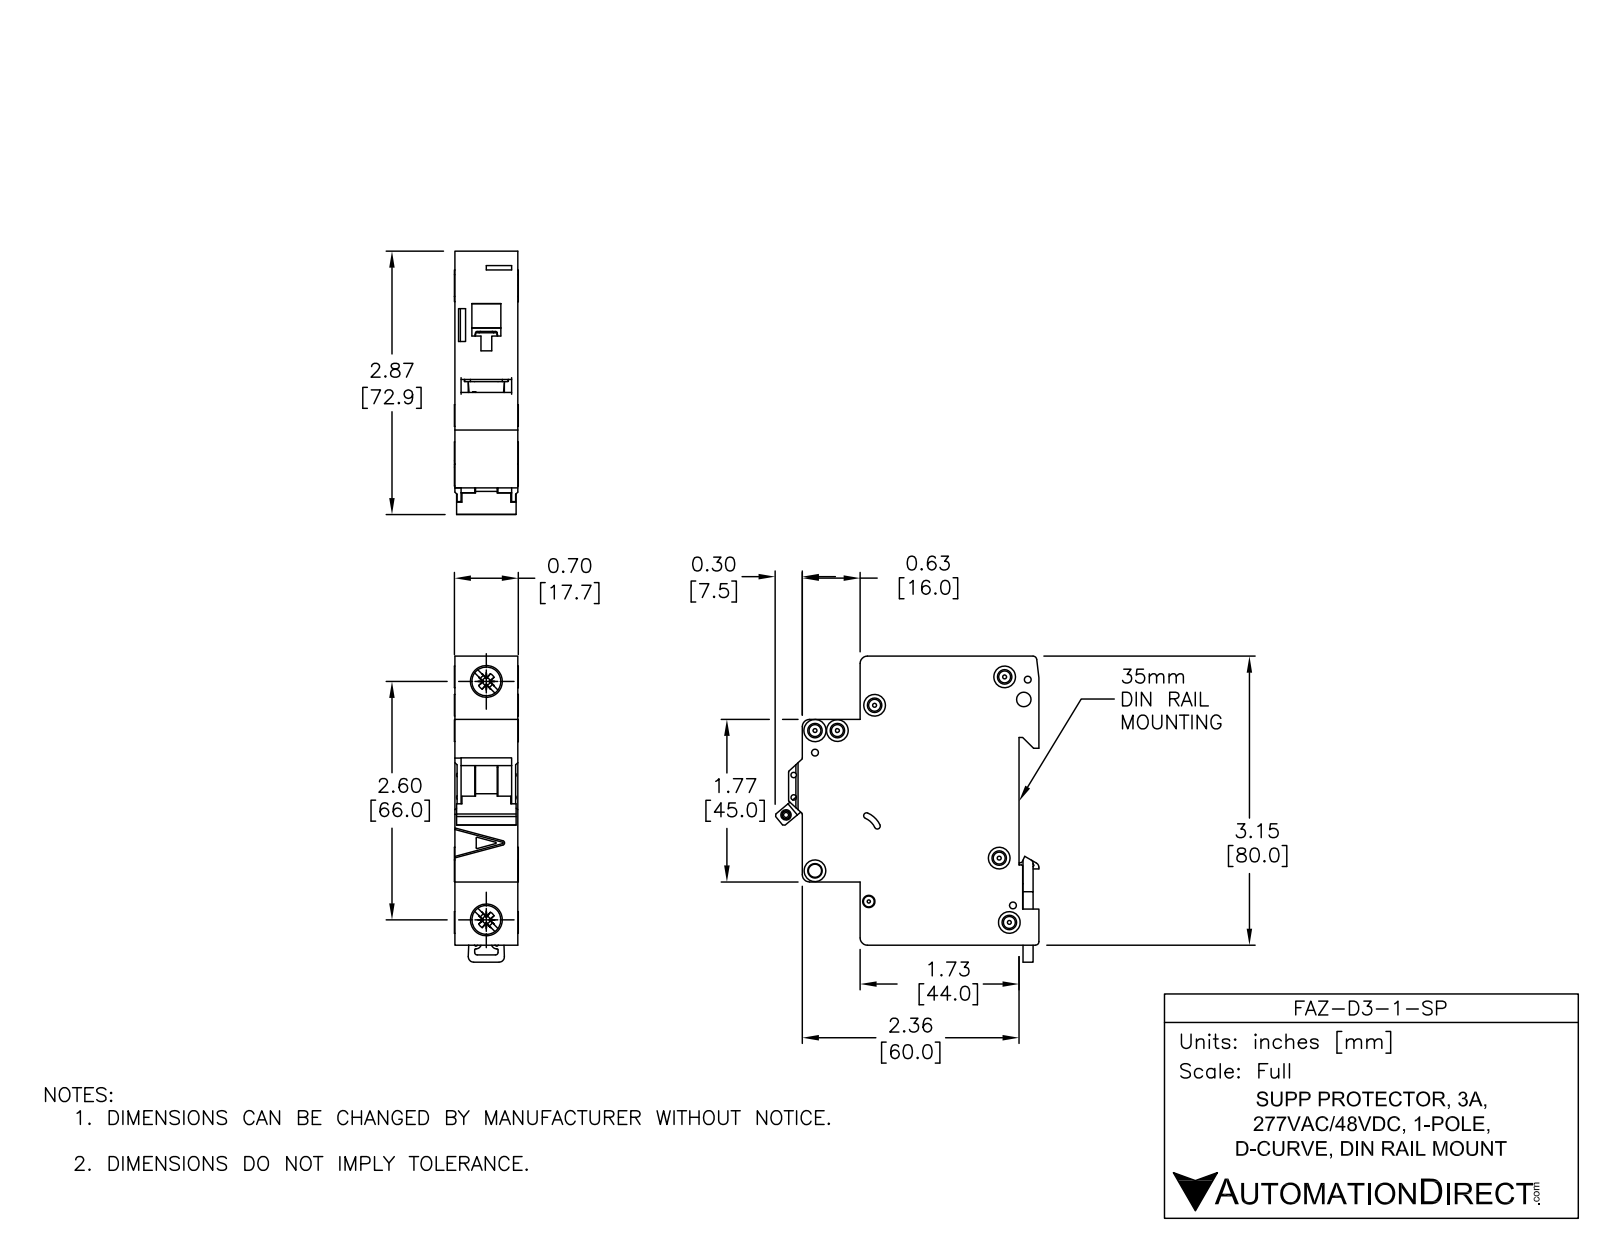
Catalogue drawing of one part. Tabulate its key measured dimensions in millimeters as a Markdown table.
| quantity | value |
| --- | --- |
| part name | FAZ-D3-1-SP |
| STEP written by | SolidWorks 2014 (AUTOMOTIVE_DESIGN) |
| units | millimeters |
| bodies | 5 solids, 558 faces (235 planar, 202 cylindrical, 121 other) |
| overall size | 84.78 × 73.04 × 17.7 |
| volume | 74 935 mm³ |
| surface area | 19 545 mm² |
| round holes (diameter × count) | 3.6 × 6, 1.9 × 3, 1.09 × 2, 1.5 × 2, 4 × 2, 7.15 × 2, 2.15 × 1, 2.2 × 1, 2.55 × 1, 3.3 × 1, 3.4 × 1 |
| round bosses / shafts (diameter × count) | 6 × 4, 8.2 × 2, 2.5 × 1 |
| partial cylindrical surfaces (radius × count) | 0.25 × 30, 0.5 × 13, 2 × 8, 0.2 × 5, 1 × 4, 0.8 × 2, 3 × 2, 1.5 × 1 |
| main face-to-face distances | 17.5, 79.48, 5.5, 49.5, 44, 65.5, 60, 16, 1.75, 15.75 |
| hole center spacings | 6.2, 13.64, 4.81, 5.19, 5.61, 6.1, 6.44, 8.19 |
